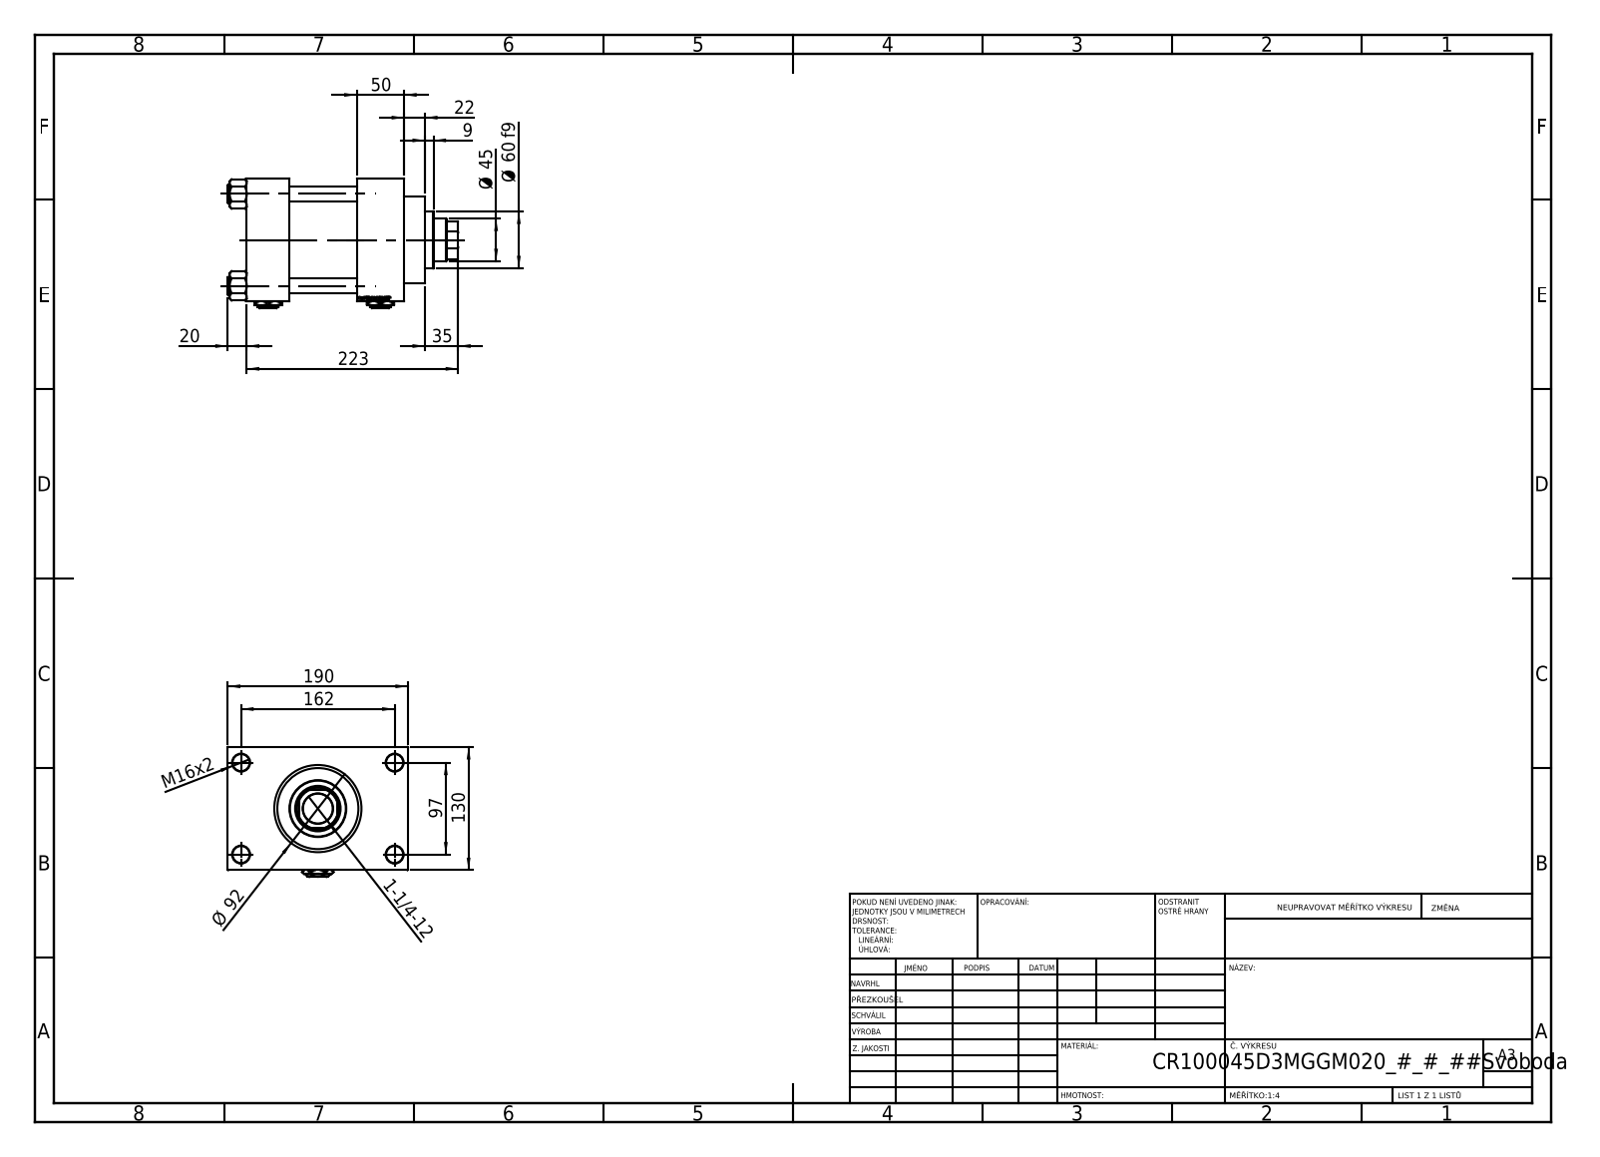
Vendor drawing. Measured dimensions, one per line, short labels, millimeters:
name: NUT_M5_D; V215CR_D_TYCINKA; Zatka_pro_OIL_PORT; V215CR_D_Body (+2 more)
written by: SolidWorks 2019 (CONFIG_CONTROL_DESIGN)
unit: mm
bodies: 13 solids, 1253 faces (593 planar, 100 cylindrical, 560 other)
size: 243 × 190 × 137
volume: 2 592 000 mm³; area: 359 312 mm²
holes: 4× ⌀16, 4× ⌀18, 2× ⌀7, 2× ⌀26.44, 2× ⌀35, 1× ⌀31.5, 1× ⌀45, 1× ⌀48, 1× ⌀76, 1× ⌀85.5, 1× ⌀100
bosses: 4× ⌀19, 1× ⌀106, 1× ⌀92, 1× ⌀60
rounds: 1× R22
face distances: 130, 45, 116, 71, 166, 121, 50, 160, 30, 20
hole spacings: 32.55, 68.52, 94.41, 96.9, 102.27, 129.45, 161.73, 97
